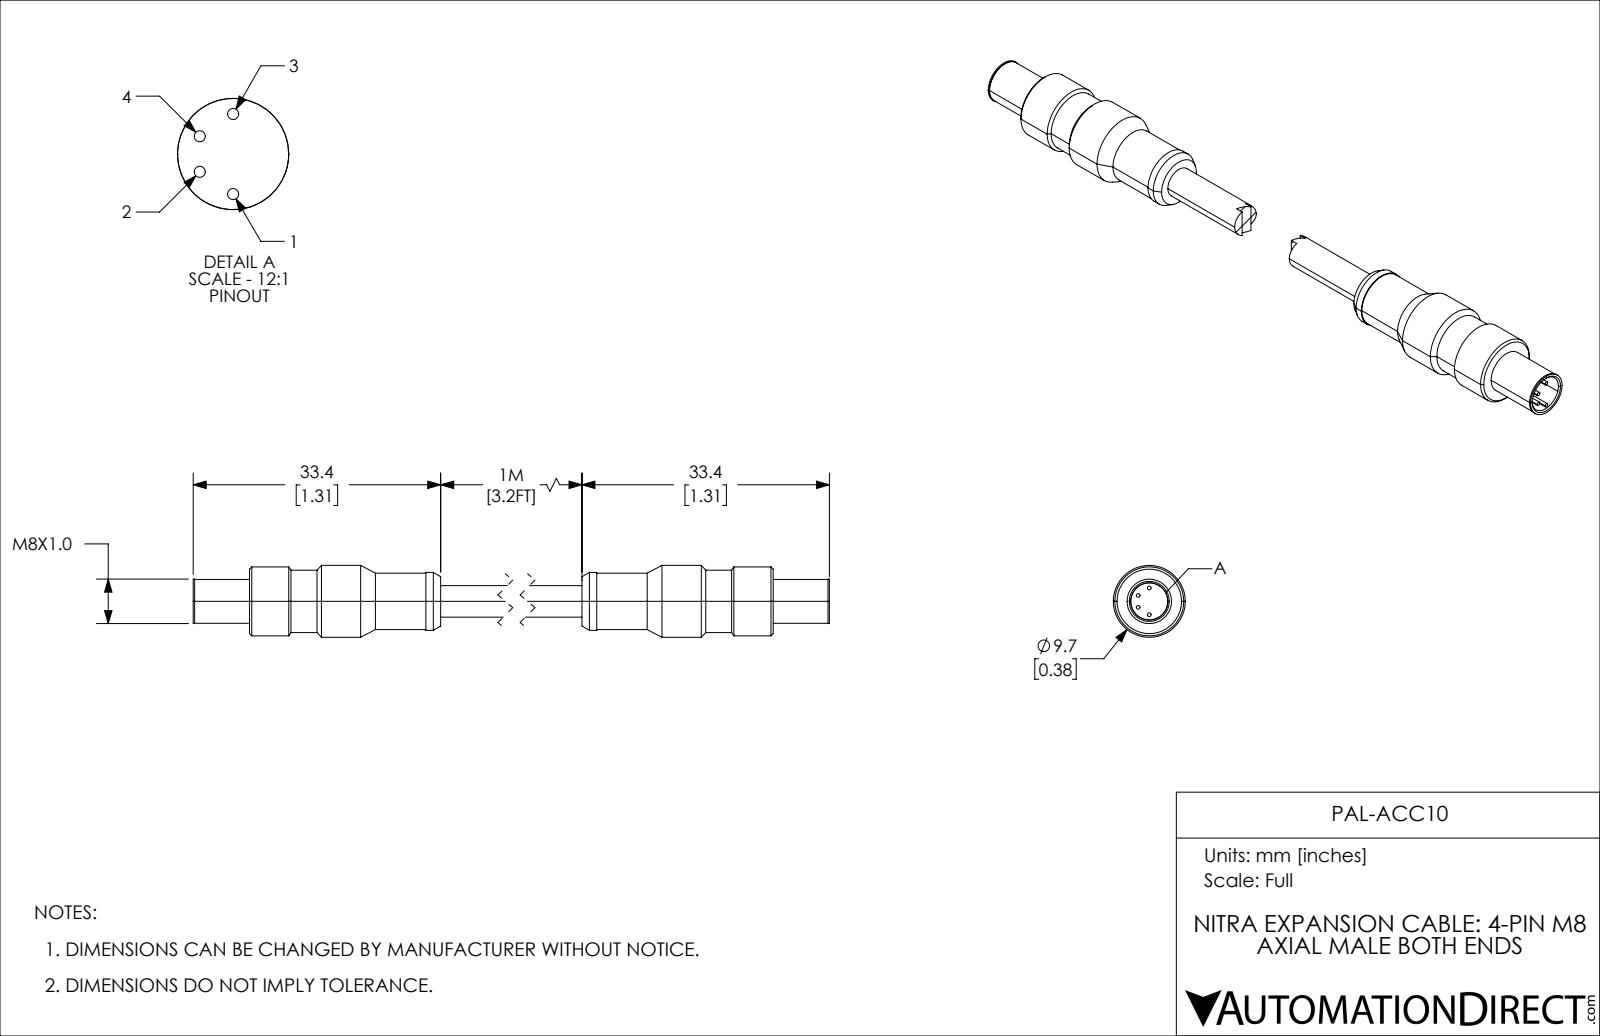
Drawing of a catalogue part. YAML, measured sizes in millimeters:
part_name: "PAL-ACC10_1"
step_written_by: "SolidWorks 2019 (CONFIG_CONTROL_DESIGN)"
units: millimeters
bodies: {solids: 1, faces: 49, planar: 11, cylindrical: 26, other: 12}
overall_size: [53.4, 9.7, 9.7]
volume: 1914
surface_area: 1341
round_holes:
  - {diameter: 5, count: 1}
round_bosses_or_shafts:
  - {diameter: 0.5, count: 4}
  - {diameter: 9.7, count: 1}
  - {diameter: 9.3, count: 1}
  - {diameter: 8.4, count: 1}
  - {diameter: 7.8, count: 1}
  - {diameter: 7.6, count: 1}
  - {diameter: 6, count: 1}
  - {diameter: 5.9, count: 1}
face_to_face_distances: [25.8, 2.6, 28.4, 48.4, 45.8, 20, 5, 7.6, 33.4, 53.4]
